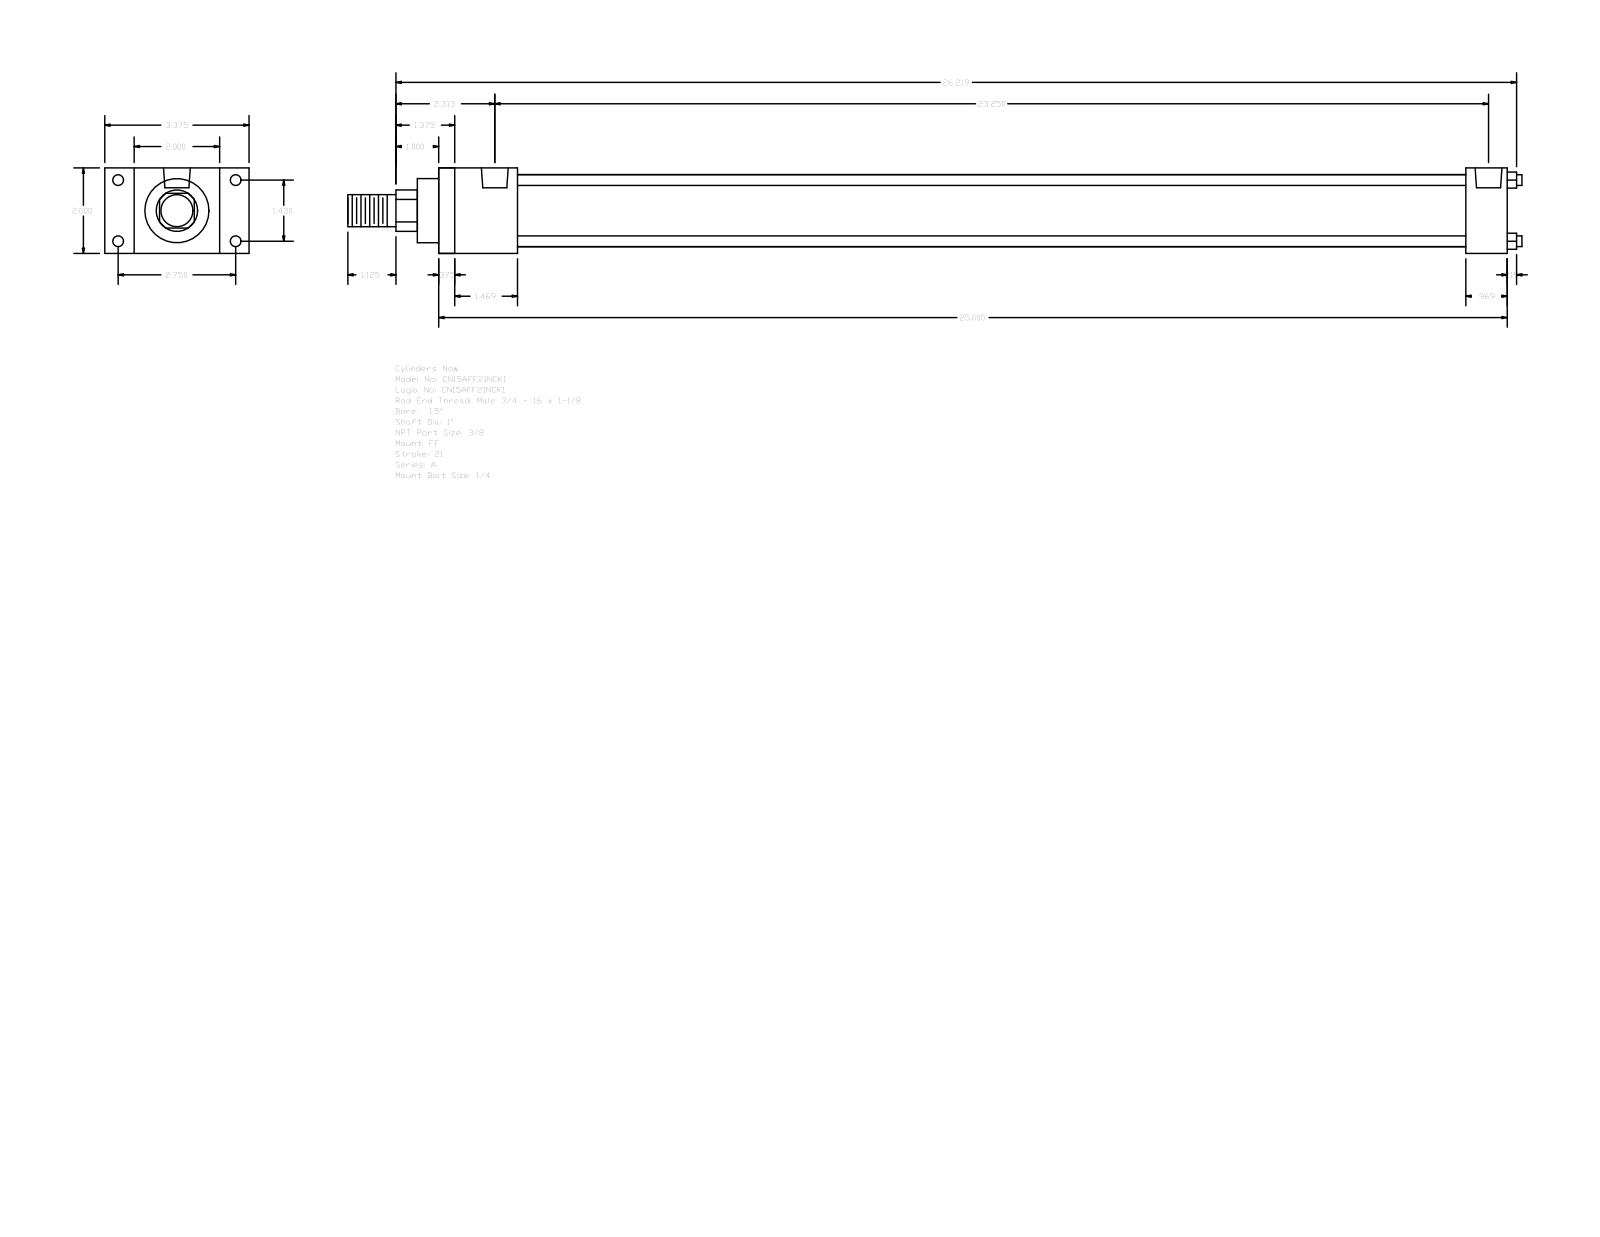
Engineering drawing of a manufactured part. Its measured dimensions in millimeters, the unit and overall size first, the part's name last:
Units: millimetres
Overall size (bounding box): 697.71 × 85.72 × 50.8
Round holes (diameter × count): ⌀5.56 ×4, ⌀6.35 ×4, ⌀15.93 ×2
Round bosses / shafts (diameter × count): ⌀6.35 ×4, ⌀42.93 ×1, ⌀38.1 ×1, ⌀25.4 ×1, ⌀19.05 ×1
Partial cylindrical surfaces — rounded edges, fillets, slot ends (radius × count): R12.29 ×1
Main face-to-face distances: 50.8, 635, 9.52, 625.48, 46.83, 610.39, 37.31, 600.87, 563.56, 588.17
Hole centre spacings: 3.97, 36.32, 69.84, 78.72, 582.61, 586.58, 590.55
Bodies: 0 solids, 92 faces (64 planar, 28 cylindrical, 0 other)
Part name (STEP PRODUCT): A_FF__0150_1
STEP written by: GSSL Pune (CONFIG_CONTROL_DESIGN)
